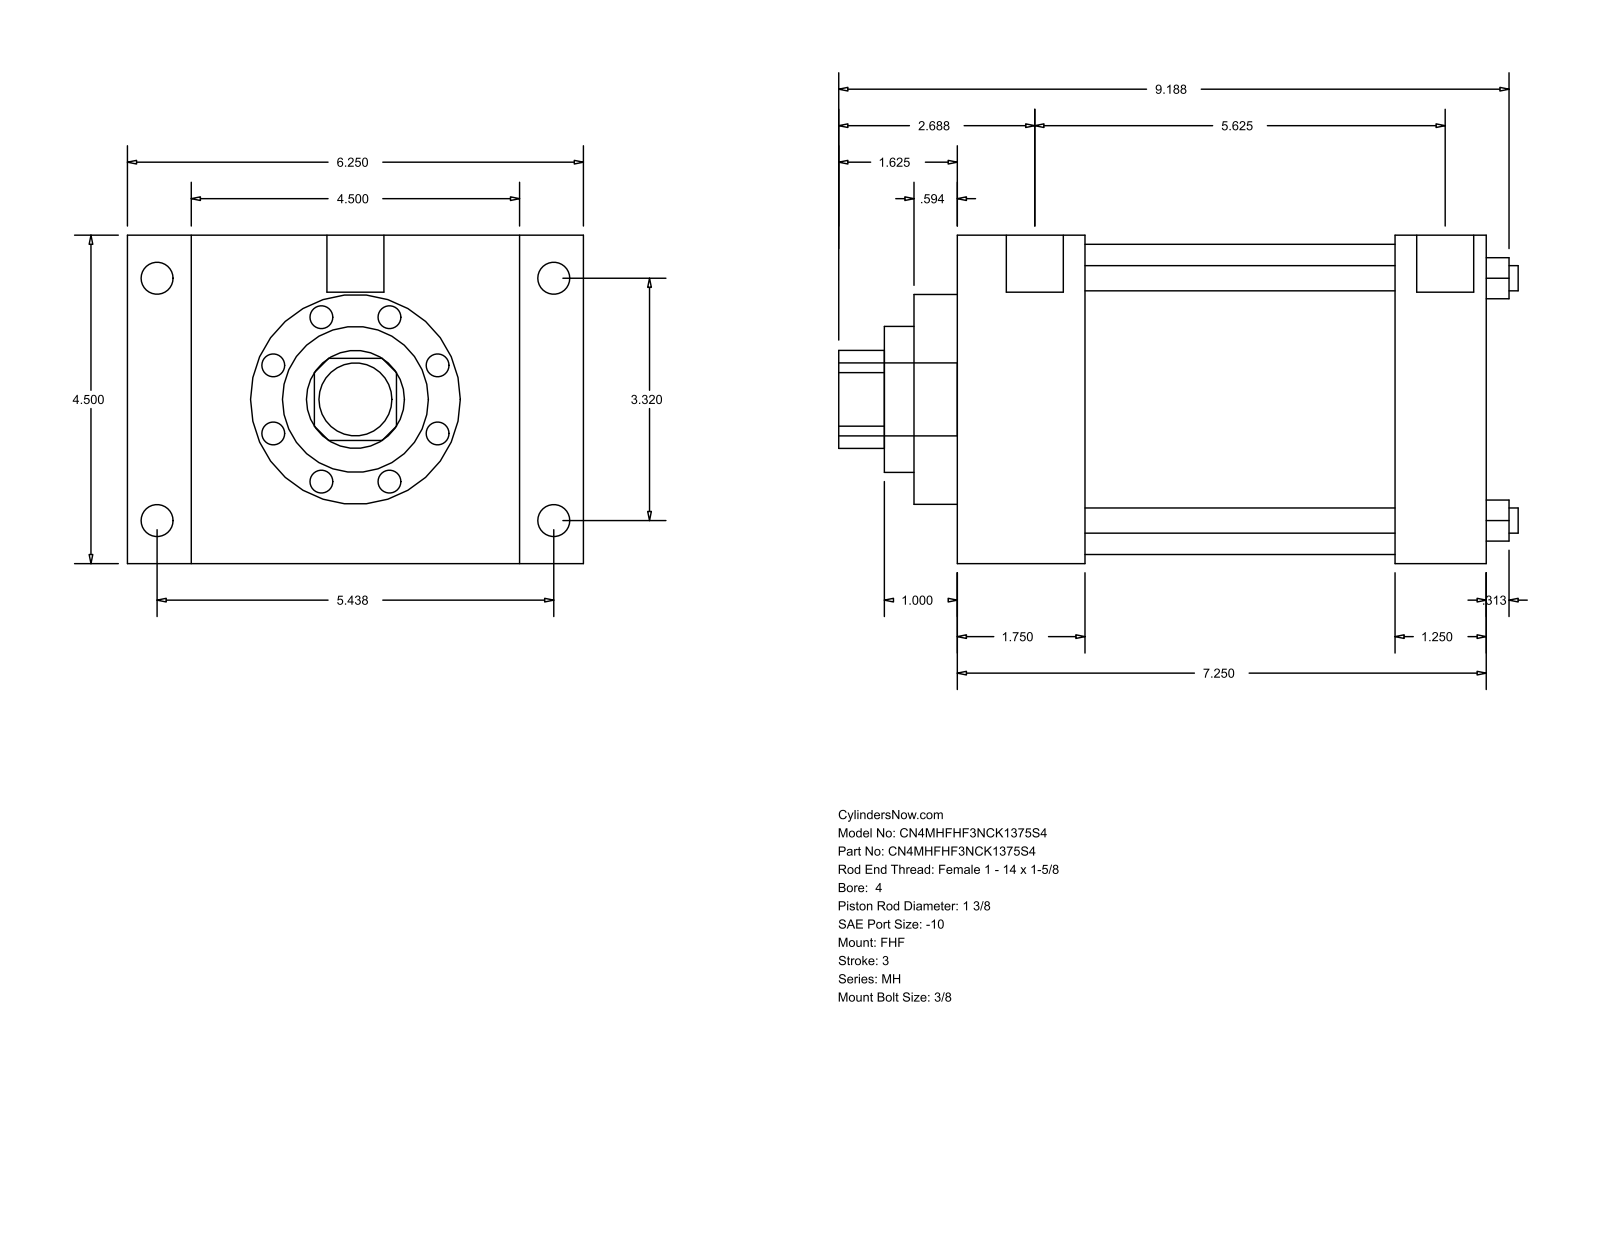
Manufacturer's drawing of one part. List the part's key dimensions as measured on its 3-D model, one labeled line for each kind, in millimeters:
Part name (STEP PRODUCT): MH_FHF__0400_1.375
STEP written by: GSSL Pune (CONFIG_CONTROL_DESIGN)
Units: millimetres
Bodies: 0 solids, 90 faces (61 planar, 29 cylindrical, 0 other)
Overall size (bounding box): 236.54 × 158.75 × 114.3
Round holes (diameter × count): ⌀8.76 ×4, ⌀34.92 ×1, ⌀50.8 ×1, ⌀73.03 ×1, ⌀107.95 ×1
Round bosses / shafts (diameter × count): ⌀11.13 ×4, ⌀8.73 ×4, ⌀19.84 ×2, ⌀25.4 ×1
Partial cylindrical surfaces — rounded edges, fillets, slot ends (radius × count): R17.06 ×1
Main face-to-face distances: 114.3, 184.16, 44.45, 139.71, 22.23, 136.53, 158.76, 152.41, 107.96, 31.75
Hole centre spacings: 59.62, 84.32, 119.25
